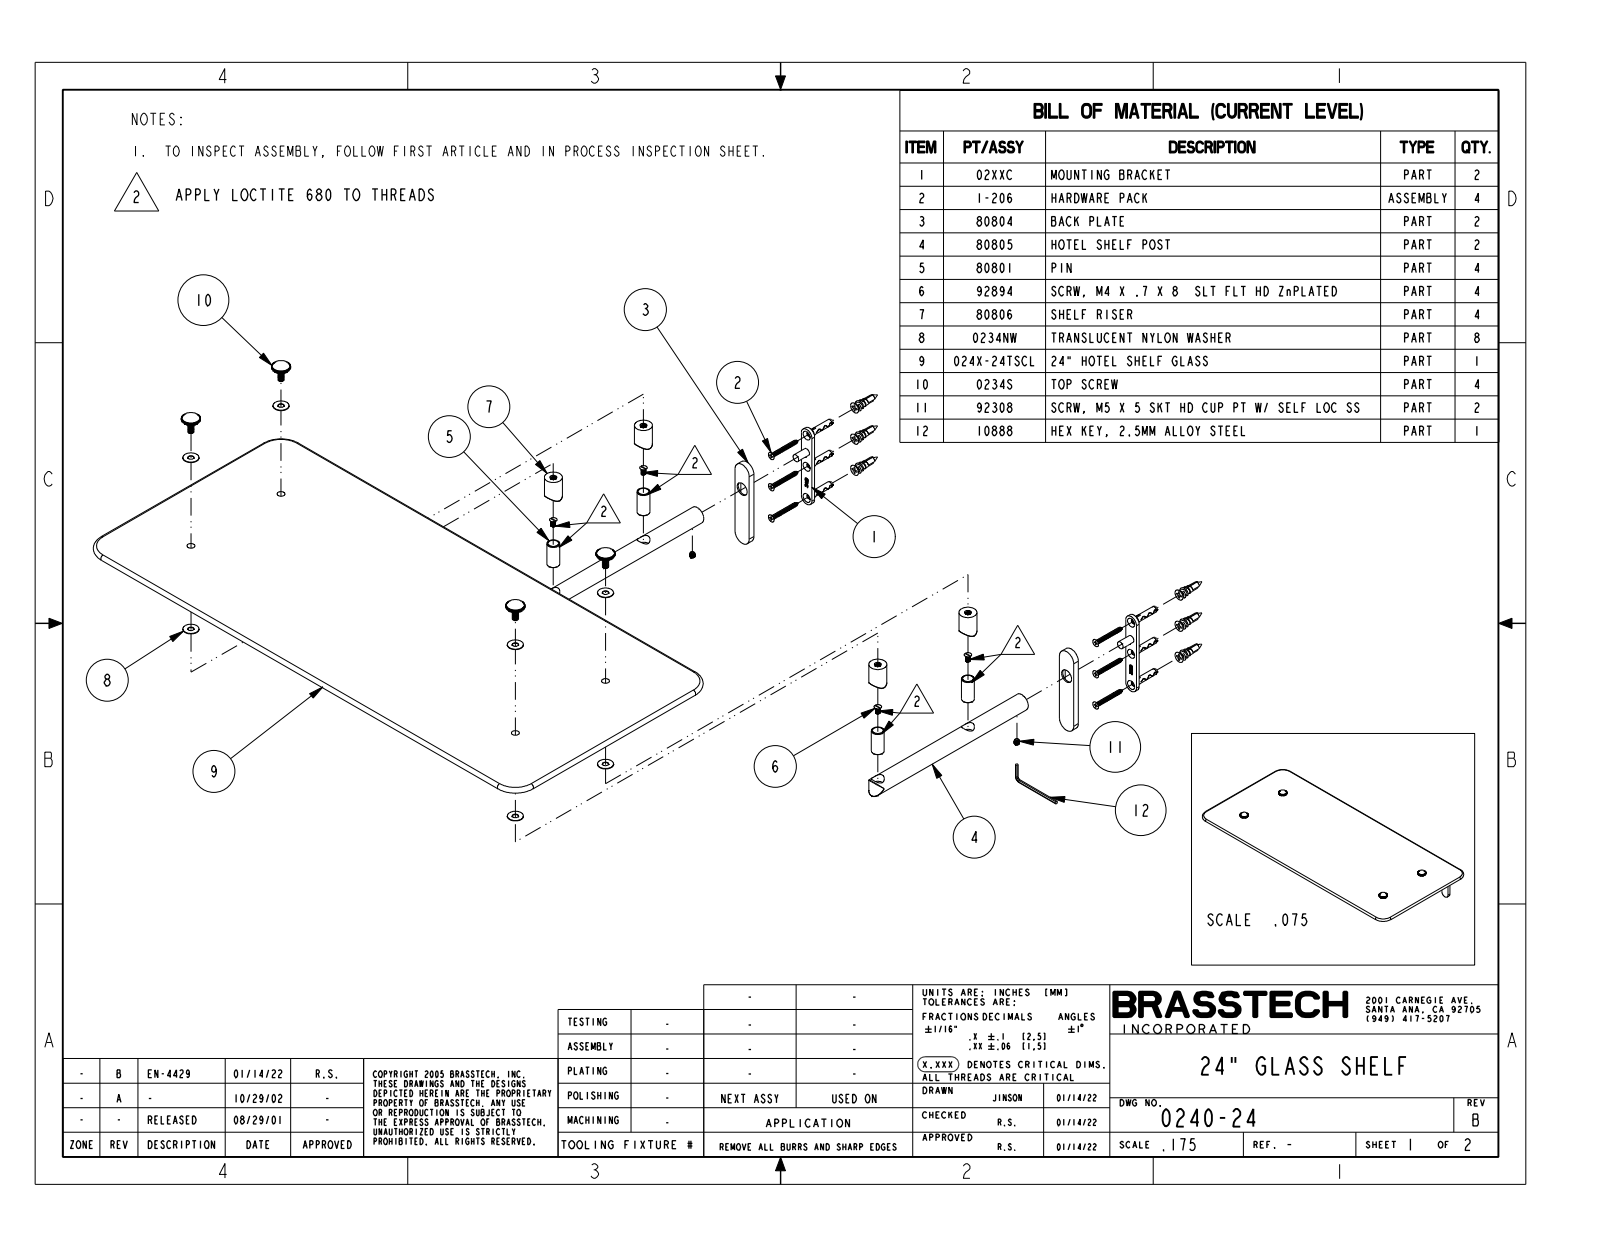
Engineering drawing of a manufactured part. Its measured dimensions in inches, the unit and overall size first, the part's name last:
Units: inches
Overall size (bounding box): 24 × 11.248 × 4.254
Round holes (diameter × count): ⌀0.512 ×4
Round bosses / shafts (diameter × count): ⌀0.708 ×4, ⌀0.63 ×4, ⌀0.508 ×4, ⌀0.709 ×2
Partial cylindrical surfaces — rounded edges, fillets, slot ends (radius × count): R0.125 ×4, R0.375 ×4, R0.394 ×4, R0.354 ×2, R0.453 ×2
Main face-to-face distances: 0.25, 0.256, 0.368, 0.118, 18, 0.787, 18.787, 17.213, 0.02, 0.27
Hole centre spacings: 5, 18, 18.681
Volume: 74.96 in³ · Surface area: 599.6 in²
Bodies: 1 solid, 984 faces (602 planar, 346 cylindrical, 36 other)
Part name (STEP PRODUCT): 0240-24
STEP written by: CREO PARAMETRIC BY PTC INC, 2018400 (CONFIG_CONTROL_DESIGN)
